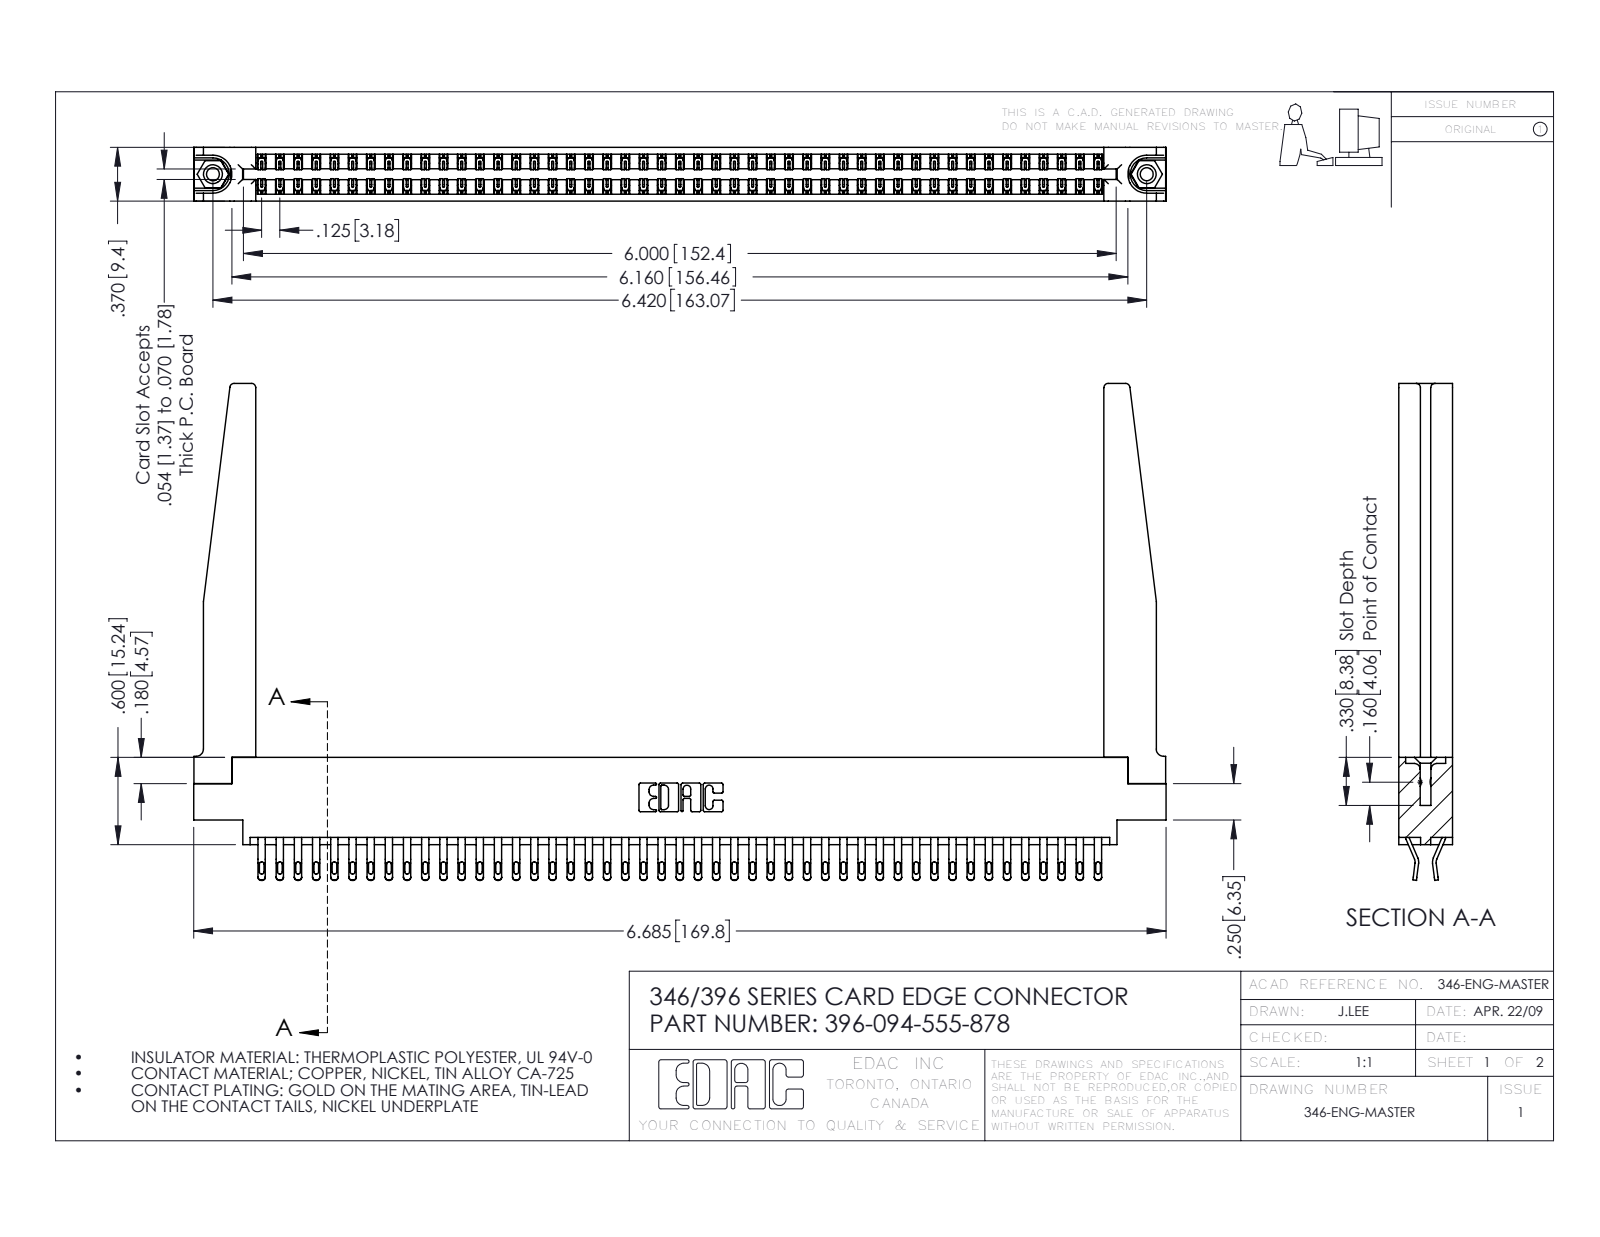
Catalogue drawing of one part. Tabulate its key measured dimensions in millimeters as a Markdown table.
| quantity | value |
| --- | --- |
| part name | 345-292-001_555 Tail; 346-220-078_345-220-078; 396-094-555-878; 346 Part_0.170 Offset - 0.156 Dia-TH (+1 more) |
| STEP written by | SolidWorks 2016 (CONFIG_CONTROL_DESIGN) |
| units | millimeters |
| bodies | 99 solids, 5812 faces (3324 planar, 2436 cylindrical, 52 other) |
| overall size | 169.8 × 86.7 × 9.4 |
| volume | 23 630 mm³ |
| surface area | 30 740 mm² |
| round holes (diameter × count) | 2.3 × 2, 3.2 × 2, 4 × 2, 1.6 × 1 |
| round bosses / shafts (diameter × count) | 3.9 × 2 |
| partial cylindrical surfaces (radius × count) | 0.4 × 188, 0.5 × 188, 0.2 × 141, 0.3 × 22, 0.8 × 8, 0.2 × 6, 0.8 × 6, 1.3 × 4 |
| main face-to-face distances | 9.4, 1.2, 8.2, 1.8, 3.8, 3.8, 6.4, 0.6, 7.6, 7 |
| hole center spacings | 6.2, 157.8, 163.1 |
